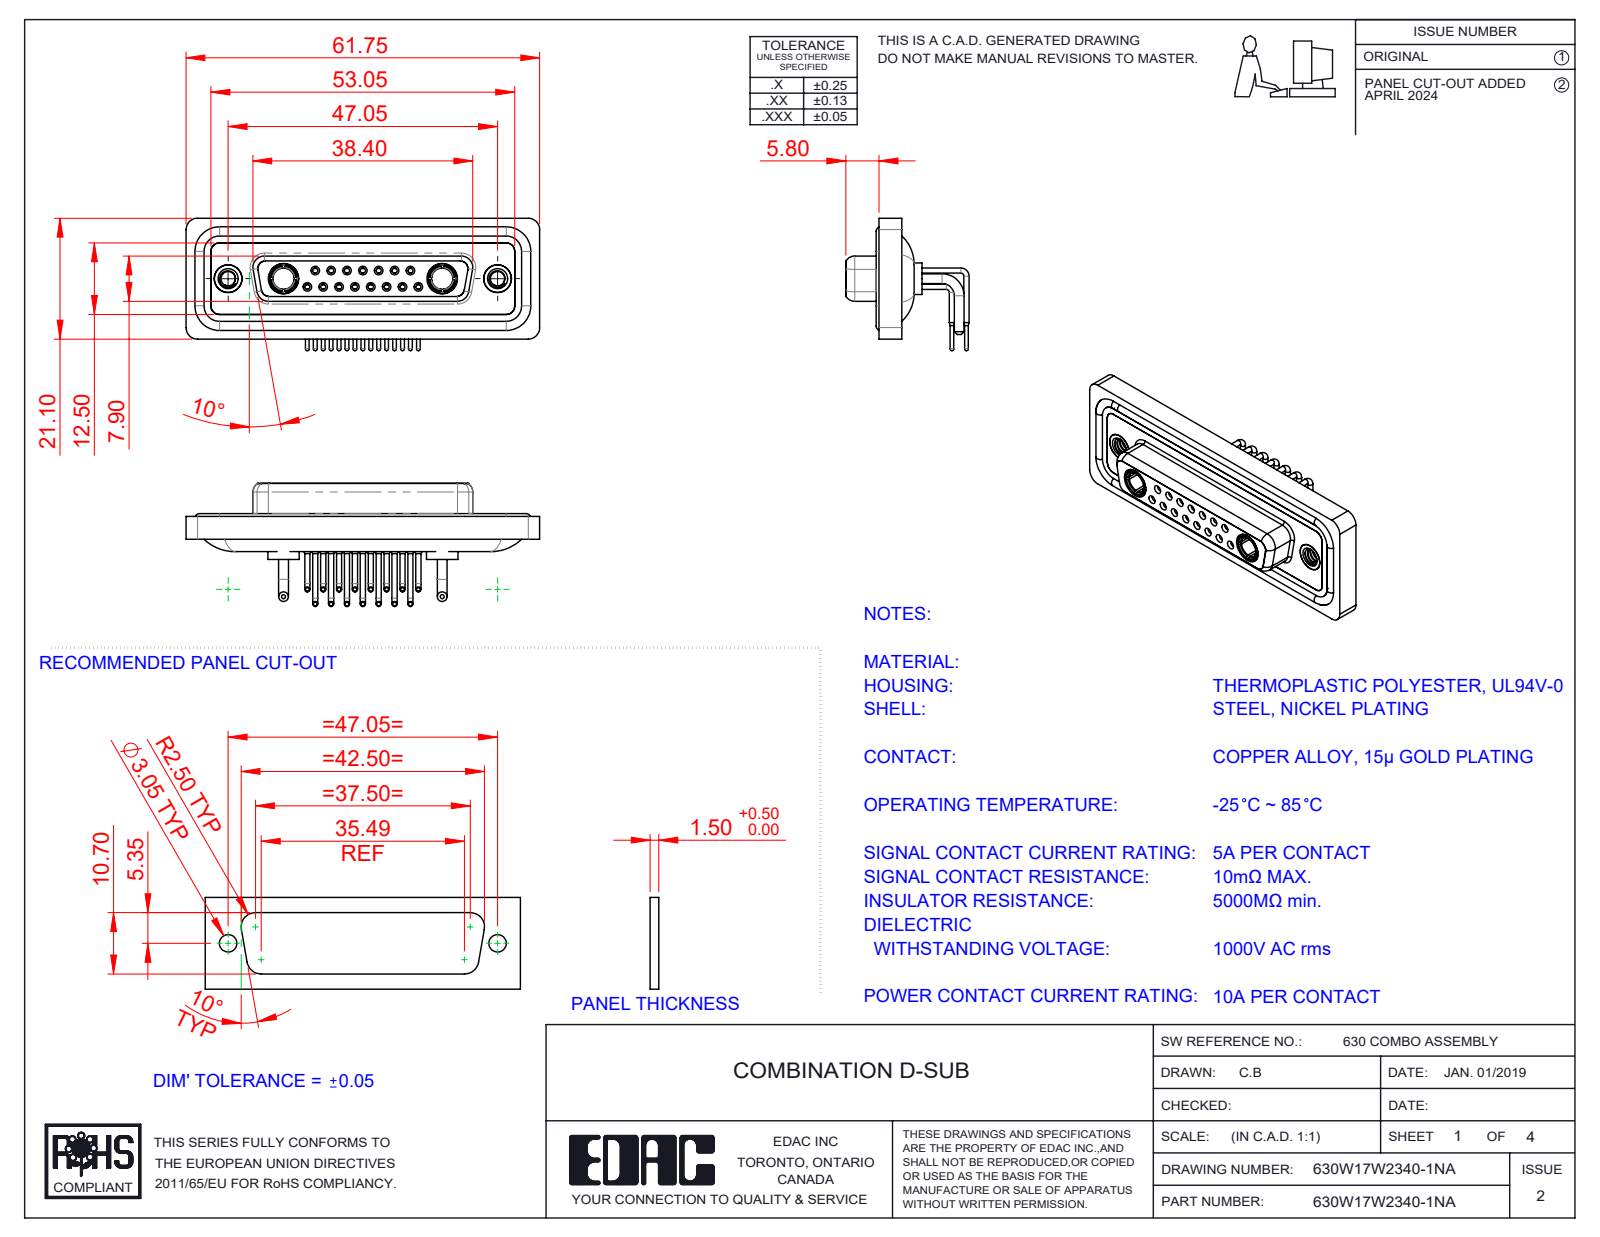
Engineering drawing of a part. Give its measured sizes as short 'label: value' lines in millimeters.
name: 630W17W2340-1NA; 630Combo Shell Front_25 Contacts; 630Combo Contact Row 2_50 Contacts; 630Combo Contact Row 1_50 Contacts (+5 more)
written by: SolidWorks 2023 (CONFIG_CONTROL_DESIGN)
unit: mm
bodies: 26 solids, 1331 faces (388 planar, 581 cylindrical, 362 other)
size: 61.75 × 23.12 × 21.53
volume: 8 364 mm³; area: 14 432 mm²
holes: 15× ⌀0.9, 15× ⌀1.1, 15× ⌀1.5, 15× ⌀2, 8× ⌀1.6, 7× ⌀1.7, 4× ⌀4.85, 2× ⌀2.5, 2× ⌀3.7, 2× ⌀4, 2× ⌀4.05, 2× ⌀5
bosses: 15× ⌀0.9, 15× ⌀0.65, 11× ⌀1.6, 4× ⌀1.7, 2× ⌀5.5, 2× ⌀5.2, 2× ⌀4.96, 2× ⌀4.95
rounds: 18× R1.5, 18× R2, 8× R1.35, 8× R1.6, 4× R0.25, 4× R0.5, 4× R0.6, 4× R0.65
face distances: 0.4, 1.8, 4.1, 1.1, 1.6, 1.5, 3.1, 2.5, 3.7, 1.4
hole spacings: 3.16, 2.77, 5.54, 8.31, 5.04, 7.49, 11.08, 5.03
